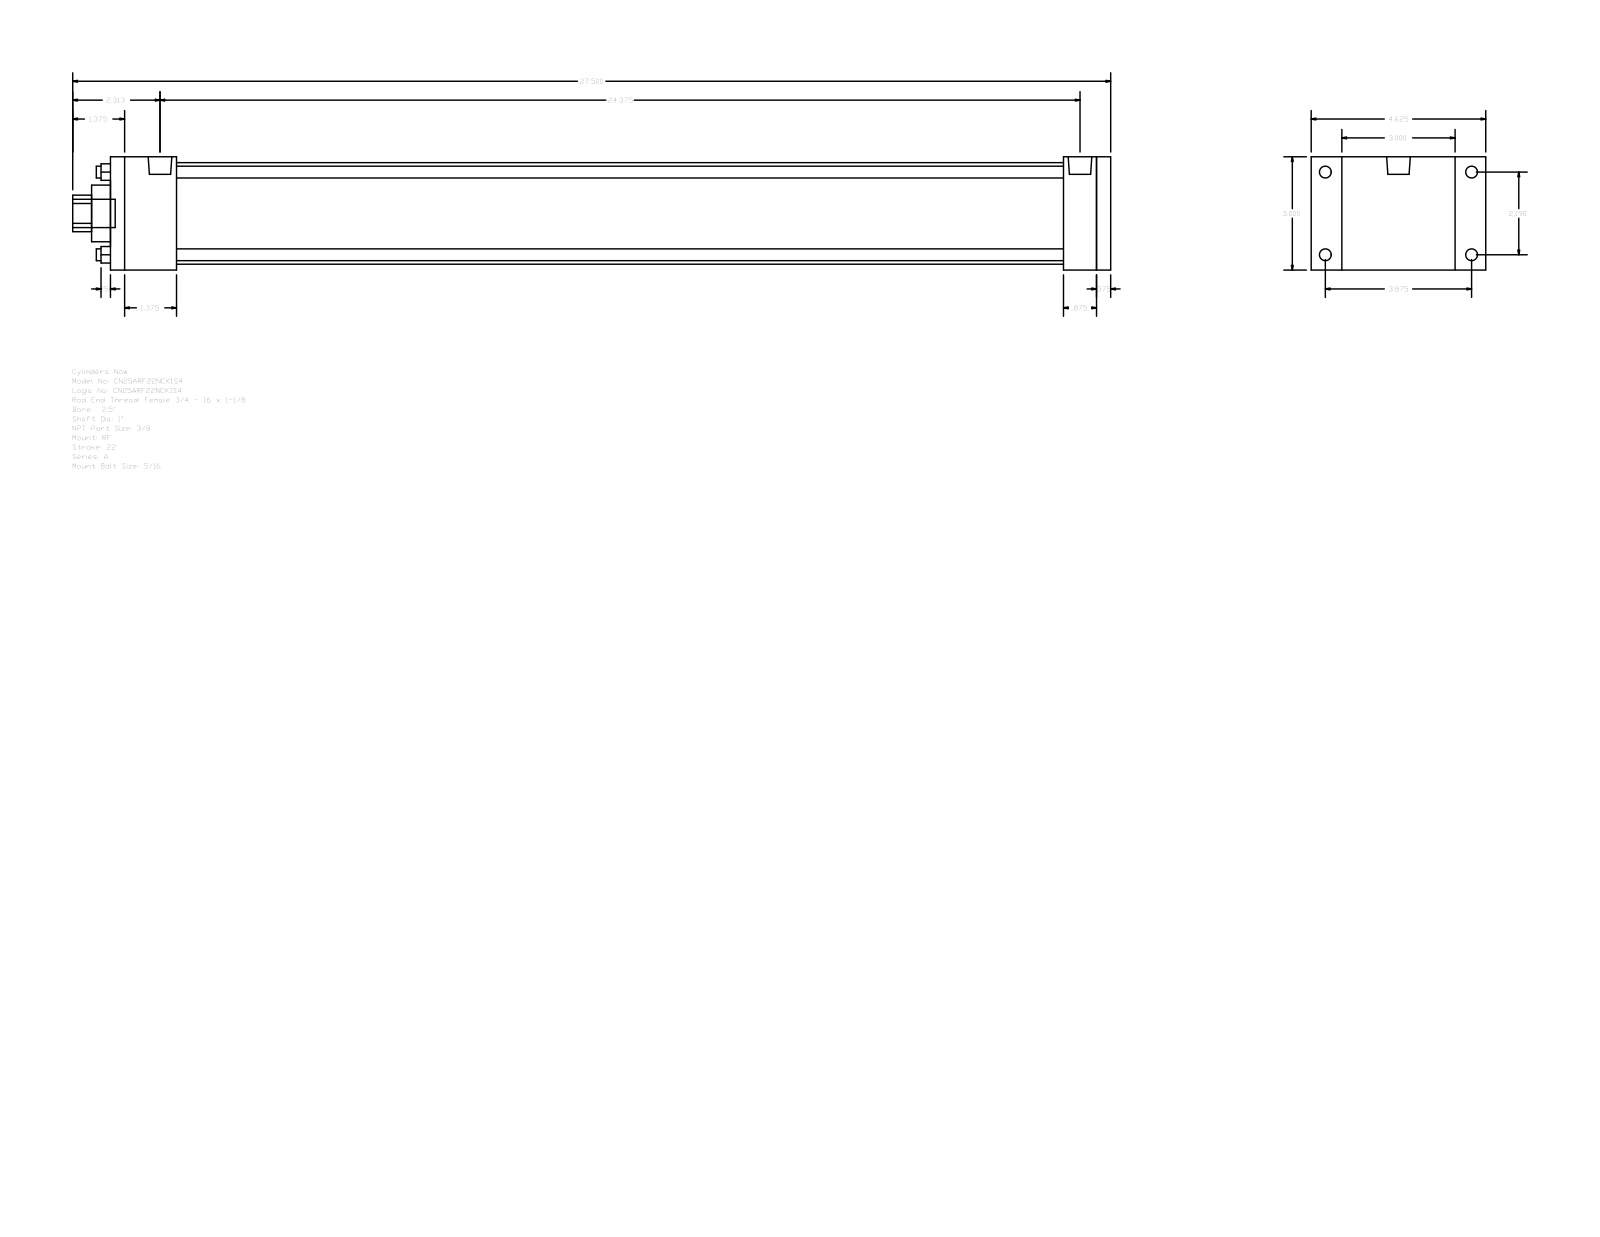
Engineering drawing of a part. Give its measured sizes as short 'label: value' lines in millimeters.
name: A_RF__0250_1
written by: GSSL Pune (CONFIG_CONTROL_DESIGN)
unit: mm
bodies: 0 solids, 92 faces (64 planar, 28 cylindrical, 0 other)
size: 698.5 × 117.47 × 76.2
holes: 4× ⌀7.94, 1× ⌀25.4, 1× ⌀38.1, 1× ⌀68.33
bosses: 4× ⌀7.94, 4× ⌀5.56, 2× ⌀15.93, 1× ⌀19.05
rounds: 1× R12.29
face distances: 76.2, 673.1, 9.52, 663.58, 44.45, 641.35, 596.9, 619.13, 628.65, 22.23
hole spacings: 39.33, 55.62, 78.66
